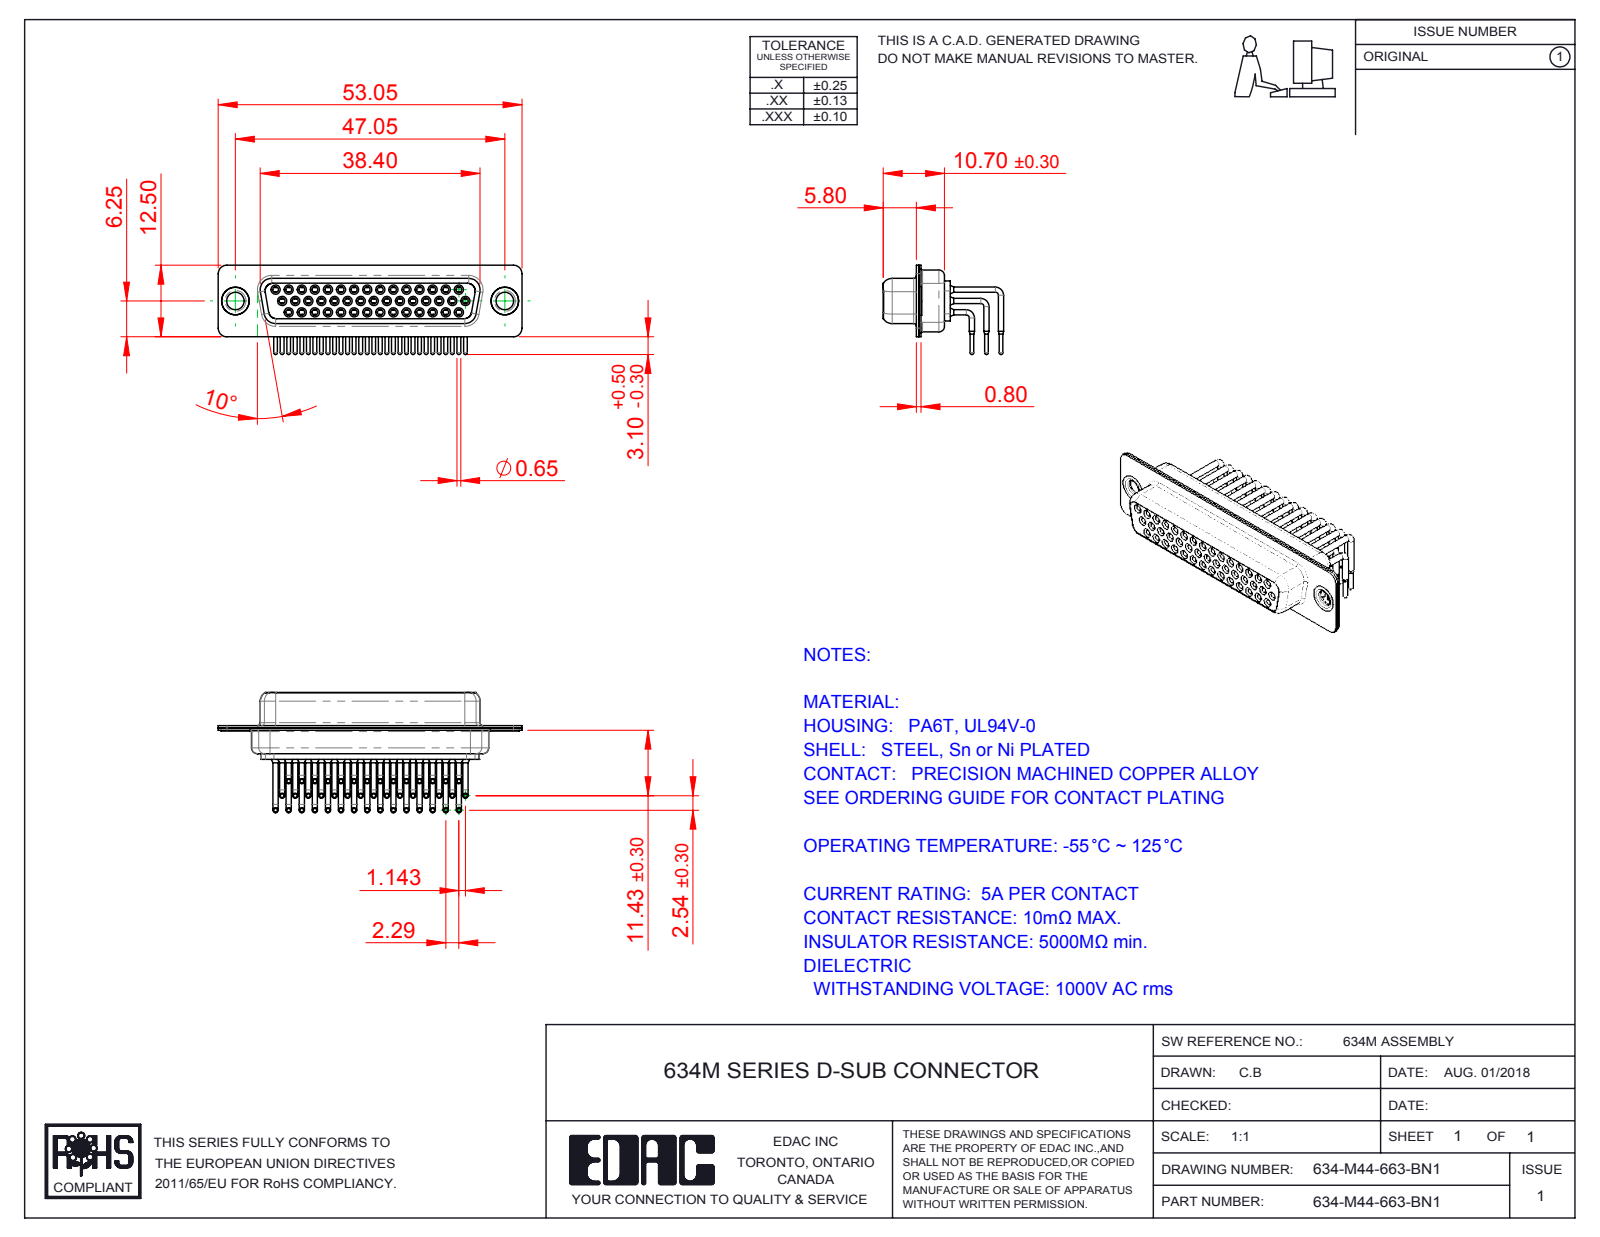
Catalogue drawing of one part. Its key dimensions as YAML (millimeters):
part_name: "634M Thru Hole Rivet; 634-M44-663-BN1; 634M Housing_44 Contacts; 634M Contact Row 3 (+4 more)"
step_written_by: "SolidWorks 2016 (CONFIG_CONTROL_DESIGN)"
units: millimeters
bodies: {solids: 49, faces: 2585, planar: 727, cylindrical: 1133, other: 725}
overall_size: [53.05, 21.02, 15.6]
volume: 3758
surface_area: 12888
round_holes:
  - {diameter: 1, count: 44}
  - {diameter: 1.1, count: 44}
  - {diameter: 1.7, count: 44}
  - {diameter: 1.8, count: 44}
  - {diameter: 2, count: 44}
  - {diameter: 3.05, count: 2}
  - {diameter: 4, count: 2}
  - {diameter: 4.8, count: 2}
round_bosses_or_shafts:
  - {diameter: 0.9, count: 88}
  - {diameter: 1.6, count: 44}
  - {diameter: 1.5, count: 44}
  - {diameter: 0.65, count: 44}
  - {diameter: 5, count: 2}
  - {diameter: 4.9, count: 2}
  - {diameter: 3.55, count: 2}
partial_cylinders:
  - {radius: 1.5, count: 16}
  - {radius: 2, count: 12}
  - {radius: 1.35, count: 8}
  - {radius: 1.6, count: 8}
  - {radius: 0.25, count: 4}
  - {radius: 0.5, count: 4}
  - {radius: 0.6, count: 4}
  - {radius: 0.65, count: 4}
face_to_face_distances: [0.4, 1.45, 8.95, 1.9, 8.5, 2.3, 6.2, 7.05, 0.45, 0.85]
hole_center_spacings: [2.28, 3.96, 2.29, 4.57, 8.24, 6.86, 11.43, 10.48]
